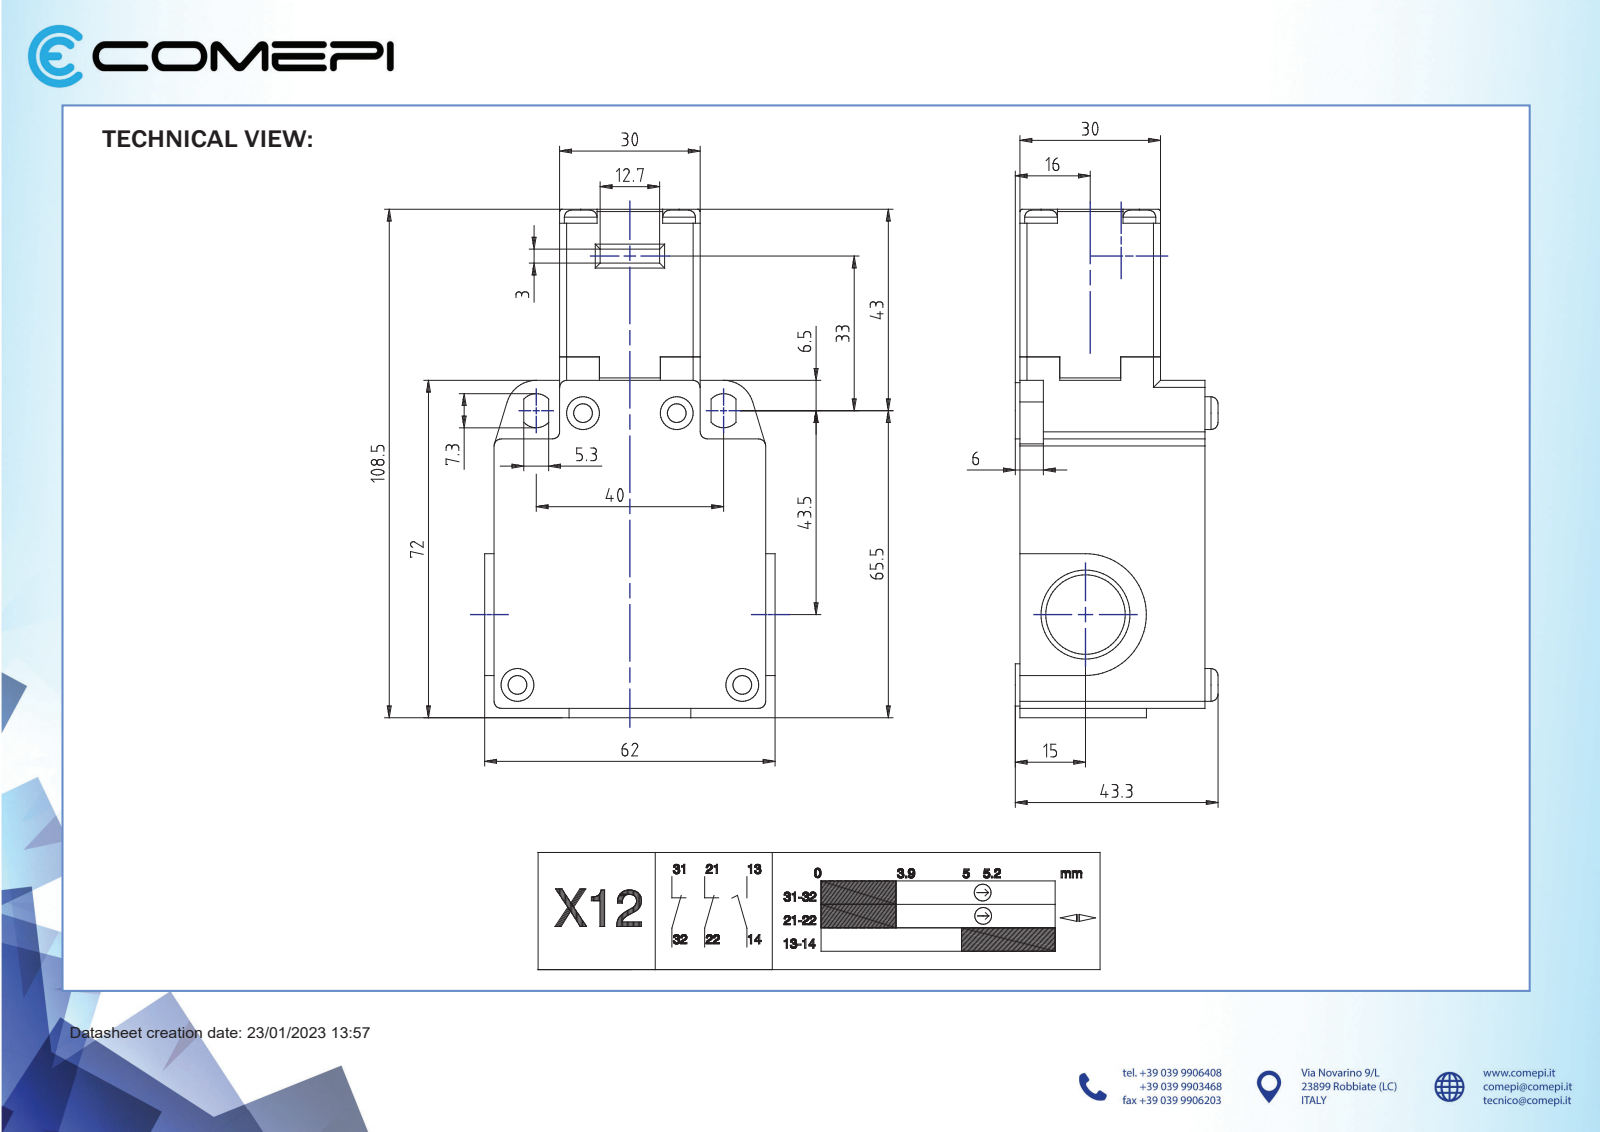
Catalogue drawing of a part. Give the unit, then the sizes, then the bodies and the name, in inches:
Units: inches
Overall size (bounding box): 4.272 × 2.441 × 1.705
Round holes (diameter × count): ⌀0.276 ×4, ⌀0.669 ×2, ⌀0.748 ×2
Round bosses / shafts (diameter × count): ⌀0.276 ×4, ⌀0.472 ×2, ⌀0.354 ×2
Partial cylindrical surfaces — rounded edges, fillets, slot ends (radius × count): R0.059 ×12, R0.02 ×4, R0.144 ×2, R0.256 ×2, R0.512 ×2, R0.453 ×1, R0.472 ×1
Main face-to-face distances: 1.555, 1.732, 0.551, 1.181, 2.283, 0.079, 0.236, 0.374, 2.756, 0.118
Hole centre spacings: 0.827, 0.557, 0.613, 1.169
Volume: 10.84 in³ · Surface area: 43.53 in²
Bodies: 2 solids, 176 faces (106 planar, 59 cylindrical, 11 other)
Part name (STEP PRODUCT): SCM2K4000X12
STEP written by: SolidWorks 2021 (AUTOMOTIVE_DESIGN)
